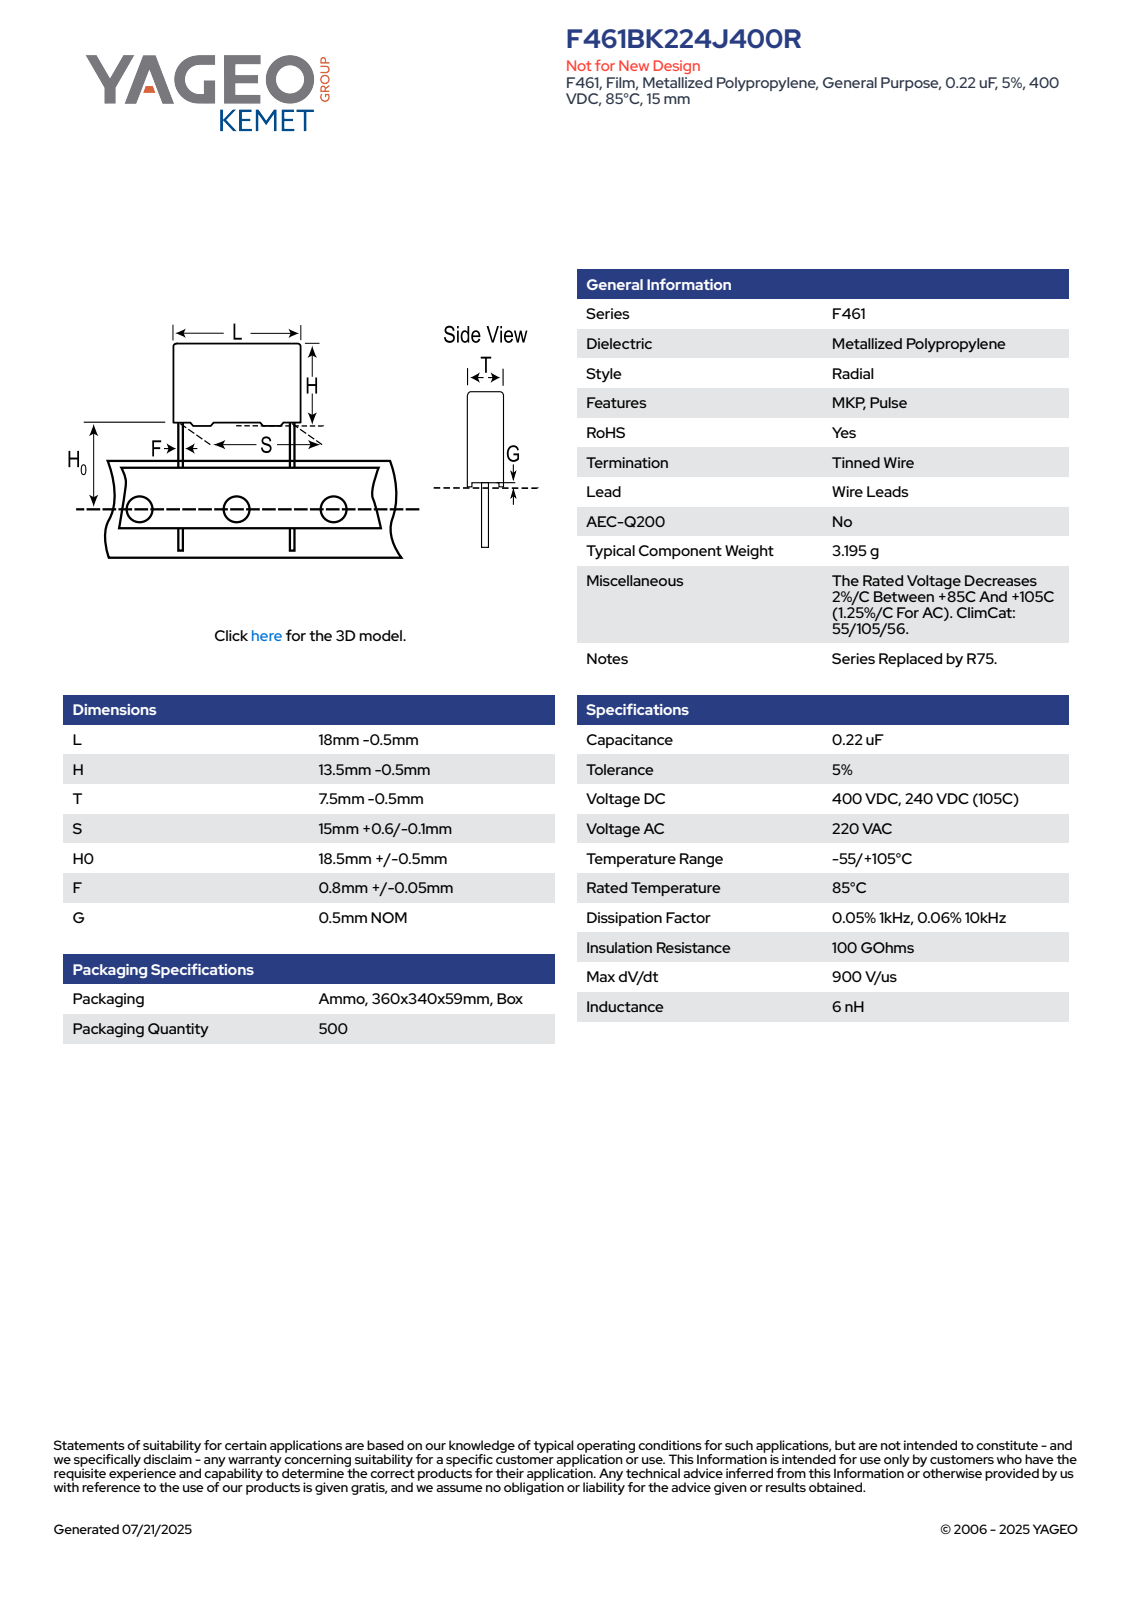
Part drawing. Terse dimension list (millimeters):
name: CFR_RBG_18X13.5X7.5_L17.5H13T7S15H019F0.85G0.5
written by: SolidWorks 2014 (AUTOMOTIVE_DESIGN)
unit: mm
bodies: 4 solids, 89 faces (81 planar, 8 cylindrical, 0 other)
size: 32 × 17.5 × 7
volume: 1 553 mm³; area: 997 mm²
bosses: 2× ⌀0.85
rounds: 4× R0.5
face distances: 7, 12.5, 17.5, 6.6, 0.4, 0.5, 13, 6.2, 19, 19.5
